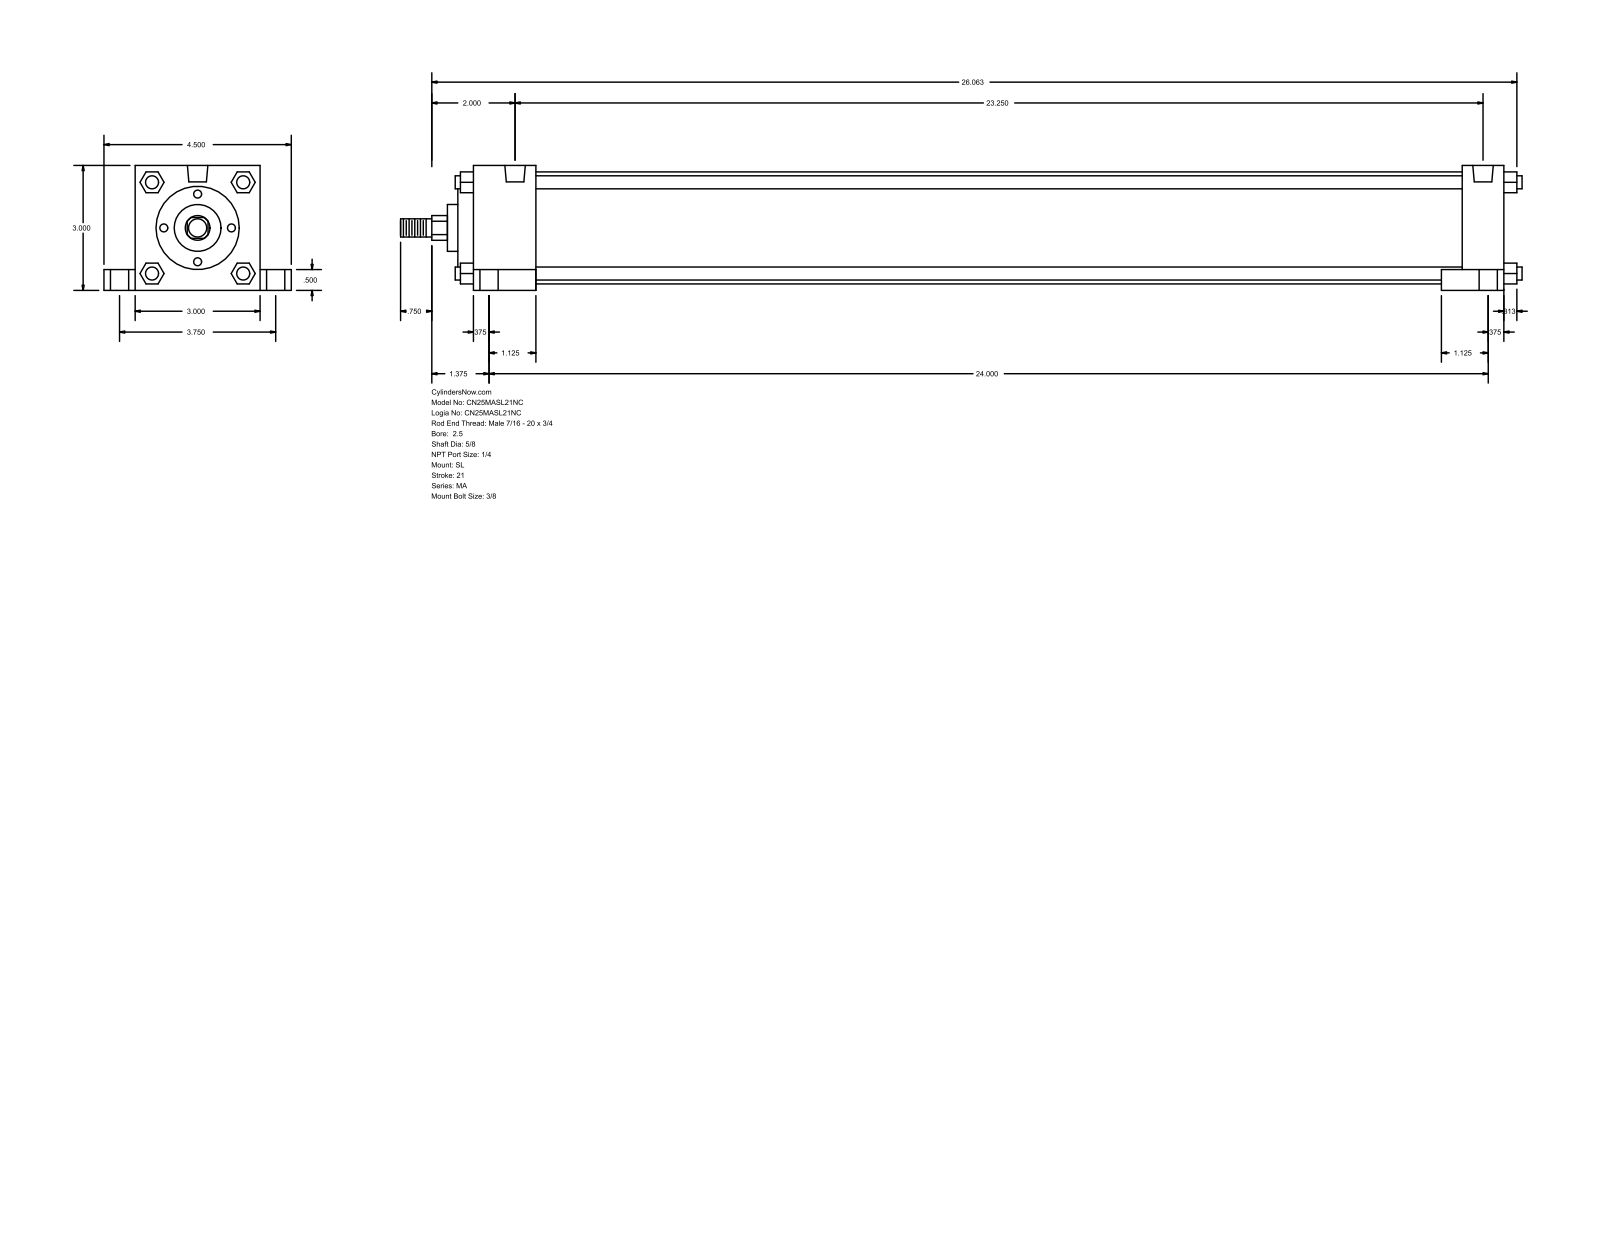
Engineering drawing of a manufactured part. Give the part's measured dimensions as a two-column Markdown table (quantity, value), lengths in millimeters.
| quantity | value |
| --- | --- |
| part name | MA_SL__0250_0.625 |
| STEP written by | GSSL Pune (CONFIG_CONTROL_DESIGN) |
| units | millimeters |
| bodies | 0 solids, 150 faces (113 planar, 37 cylindrical, 0 other) |
| overall size | 684.21 × 114.3 × 76.2 |
| round holes (diameter × count) | 7.94 × 4, 11.11 × 4, 17.46 × 4, 12.49 × 2 |
| round bosses / shafts (diameter × count) | 7.94 × 4, 68.33 × 1, 50.8 × 1, 28.57 × 1, 15.88 × 1, 11.11 × 1 |
| partial cylindrical surfaces (radius × count) | 7.54 × 1 |
| main face-to-face distances | 76.2, 628.65, 12.7, 565.15, 25.4, 38.1, 590.55, 603.25, 19.05, 63.5 |
| hole center spacings | 47.73, 50.2, 95.24, 590.55, 595.63, 608.3, 609.6, 616.99 |
